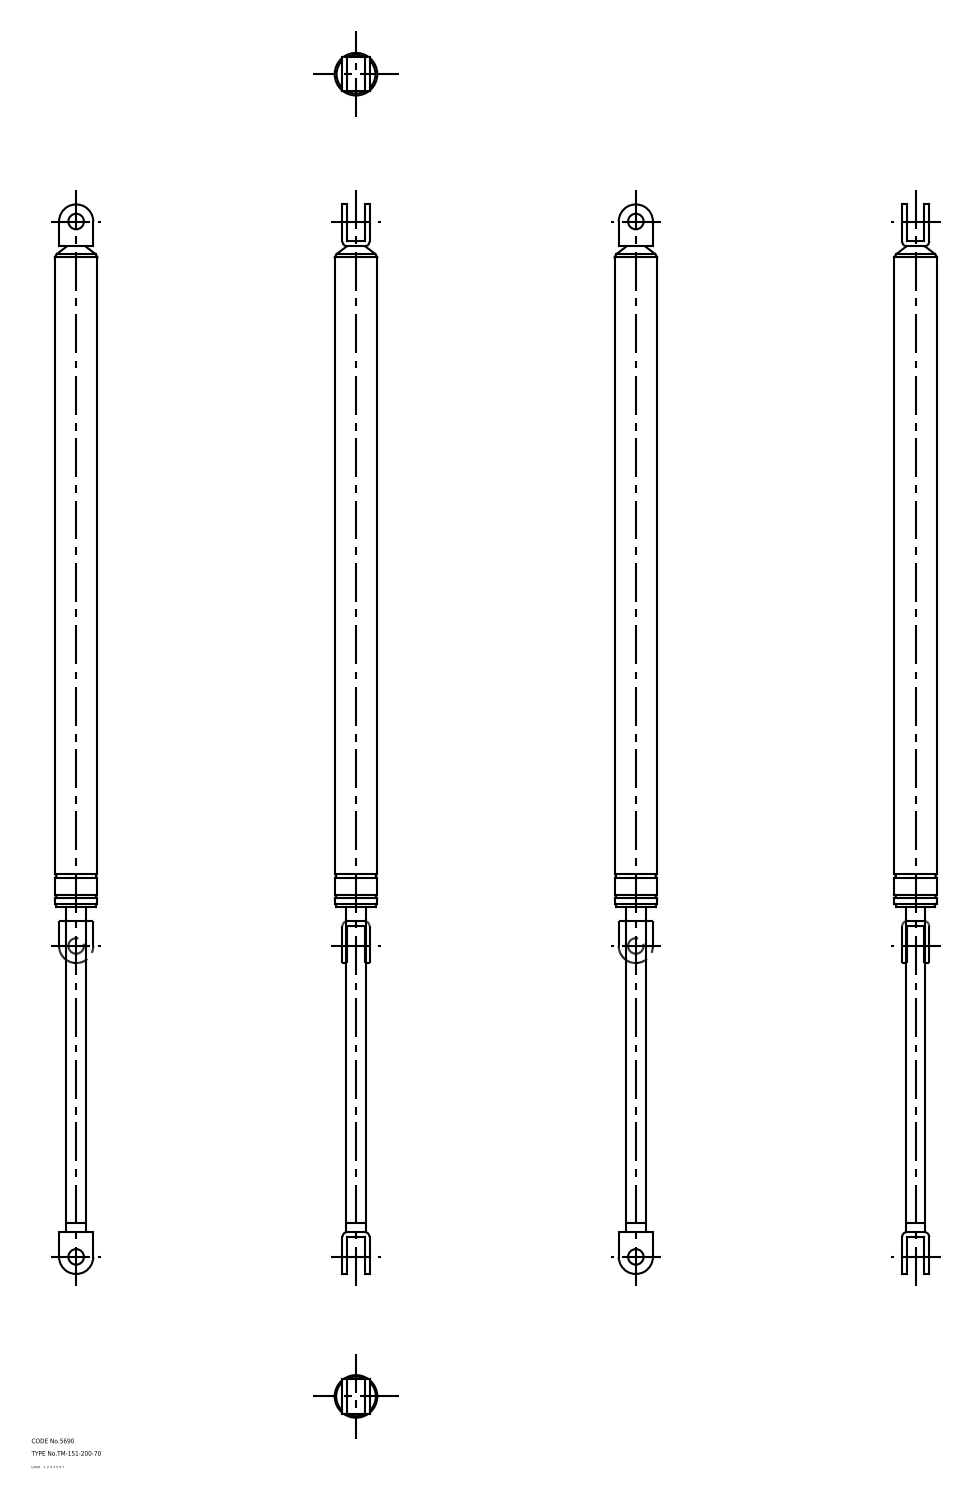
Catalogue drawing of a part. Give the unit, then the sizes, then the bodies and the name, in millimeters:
Units: millimetres
Overall size (bounding box): 688 × 27.4 × 27.4
Round holes (diameter × count): ⌀10 ×2
Round bosses / shafts (diameter × count): ⌀27.4 ×1, ⌀25.5 ×1, ⌀12.5 ×1
Partial cylindrical surfaces — rounded edges, fillets, slot ends (radius × count): R3 ×4, R11 ×2
Main face-to-face distances: 3.2, 14.2, 17.4, 11, 637.2, 22, 212.2, 640.4, 428.2, 425
Hole centre spacings: 666
Volume: 281 548 mm³ · Surface area: 51 437 mm²
Bodies: 2 solids, 63 faces (21 planar, 30 cylindrical, 12 other)
Part name (STEP PRODUCT): body_div
STEP written by: spGate 16.7.1 (AUTOMOTIVE_DESIGN)
